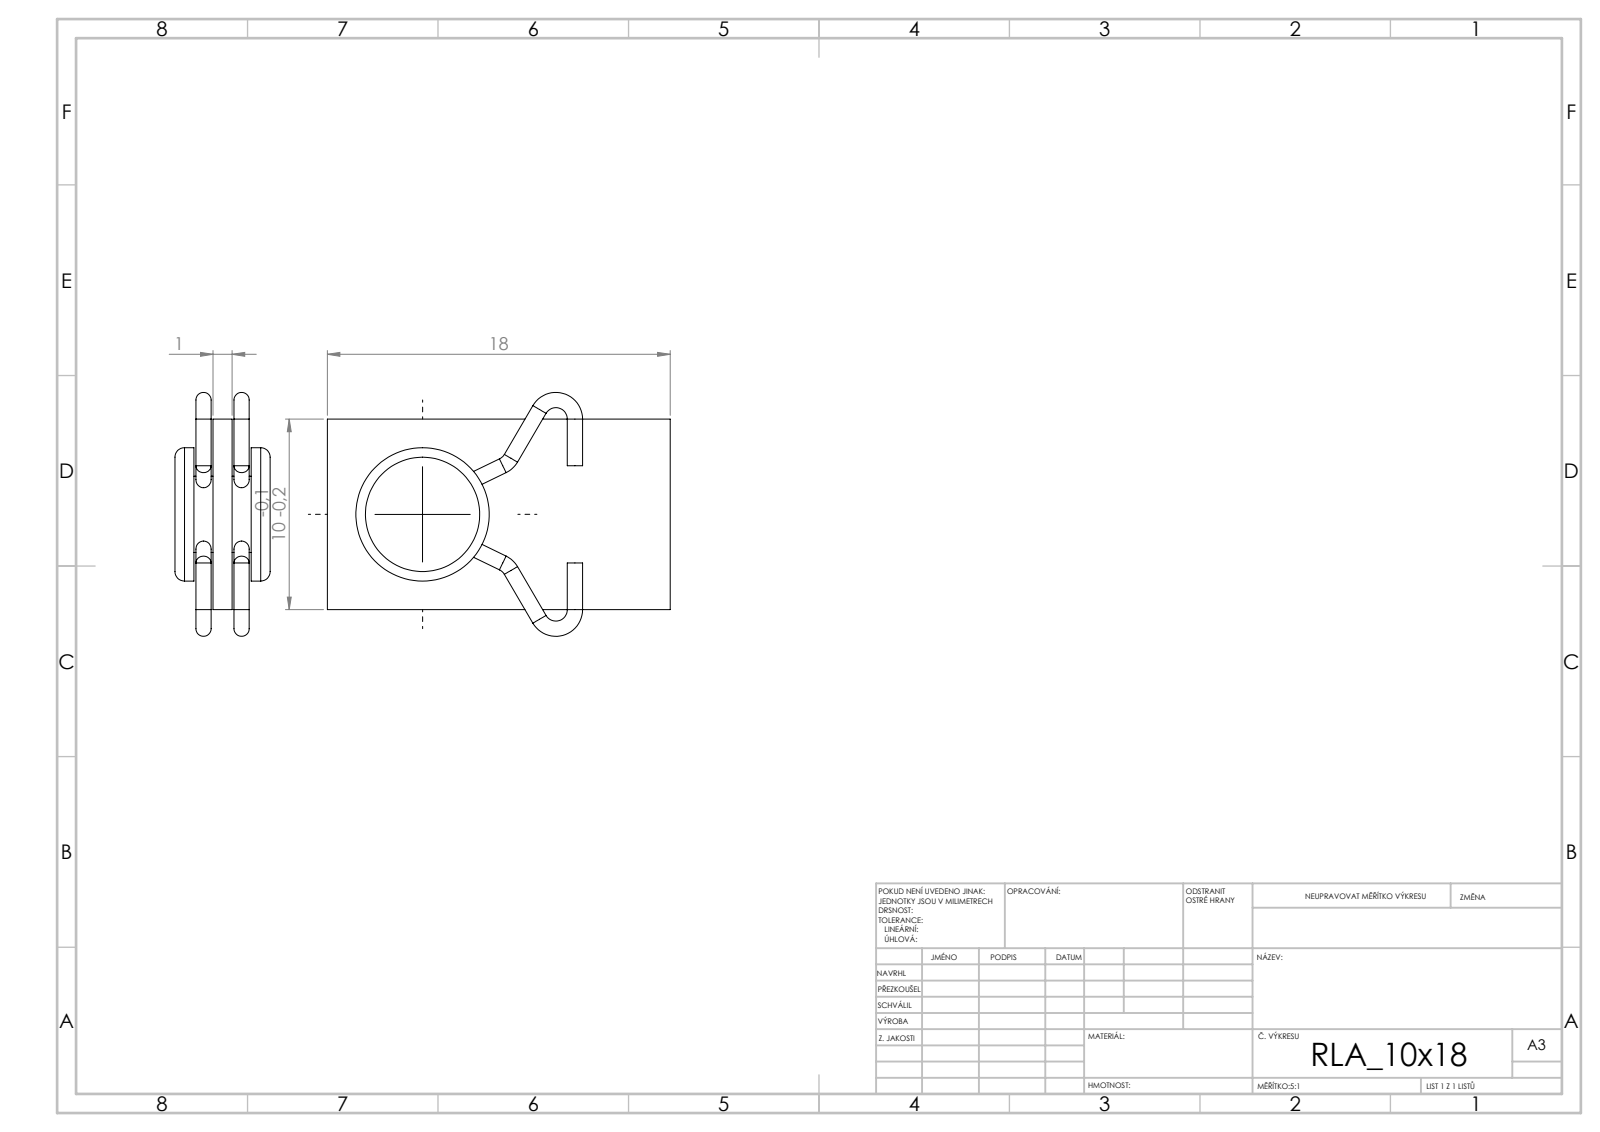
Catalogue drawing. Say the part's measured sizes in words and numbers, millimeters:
Its 3-D file was written by "SolidWorks 2019 (CONFIG_CONTROL_DESIGN)". It is 3 solids with 82 faces: 14 planar, 40 cylindrical and 28 other. Overall it measures 18 by 12.8 by 5 millimeters. Its volume is 314 cubic millimeters and its surface area 753 square millimeters. Round bosses or shafts: 14 of diameter 0.8, 1 of diameter 7, 1 of diameter 4. The main face-to-face distances are 1, 2, 3, 4, 5, 10, 18, 2.45, 7.55, 5.1.
